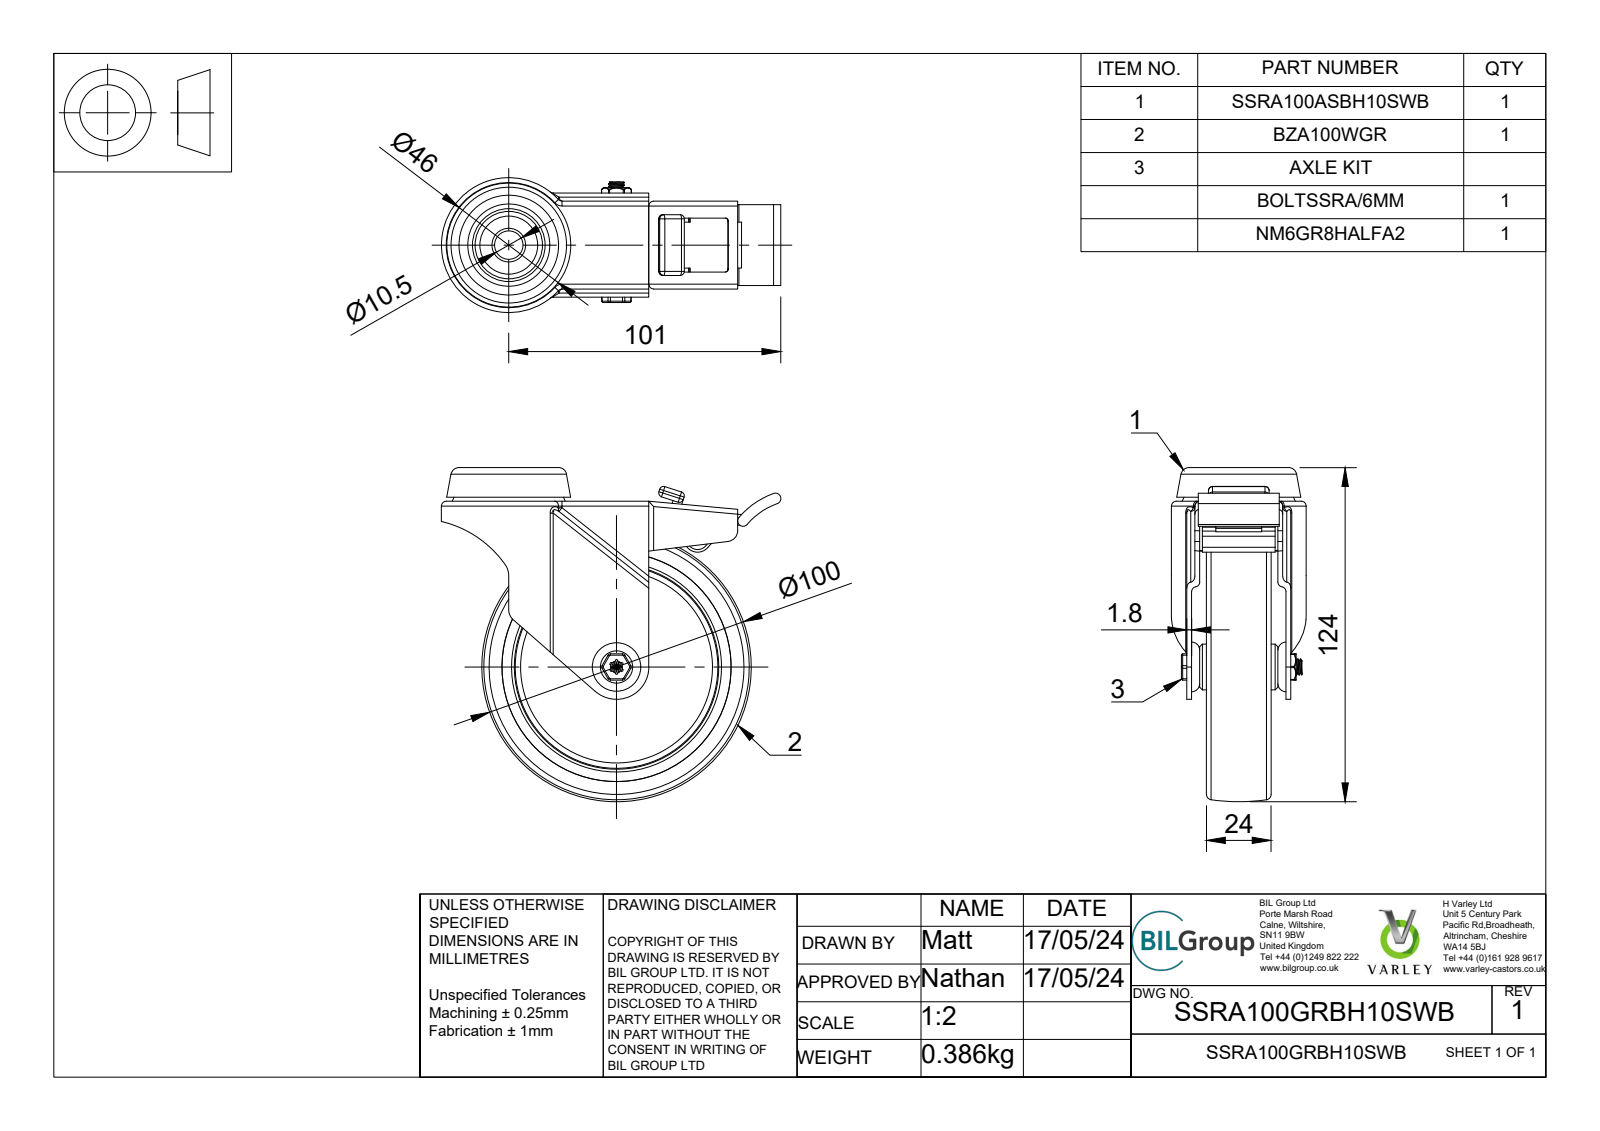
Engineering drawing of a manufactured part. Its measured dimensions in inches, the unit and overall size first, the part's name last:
Units: inches
Overall size (bounding box): 4.961 × 4.882 × 1.969
Round holes (diameter × count): ⌀0.236 ×1, ⌀0.252 ×1, ⌀0.327 ×1, ⌀0.331 ×1, ⌀0.413 ×1, ⌀0.416 ×1, ⌀1.181 ×1, ⌀3.346 ×1
Round bosses / shafts (diameter × count): ⌀1.535 ×1, ⌀0.709 ×1, ⌀0.669 ×1, ⌀0.581 ×1, ⌀0.315 ×1, ⌀0.231 ×1, ⌀0.187 ×1
Partial cylindrical surfaces — rounded edges, fillets, slot ends (radius × count): R0.071 ×27, R0.039 ×22, R0.02 ×13, R0.059 ×12, R0.016 ×6, R0.035 ×4, R0.079 ×4, R0.197 ×2
Main face-to-face distances: 0.071, 1.331, 0.354, 0.591, 0.118, 0.236, 0.453, 0.098, 0.189, 0.689
Volume: 9.257 in³ · Surface area: 129.7 in²
Bodies: 9 solids, 473 faces (199 planar, 149 cylindrical, 125 other)
Part name (STEP PRODUCT): SSRA100GRBH10SWB v4; SSRA100ASBH10SWB v1; STAINLESS STEEL HEAD (1); STAINLESS STEEL FORKS (1) (+8 more)
STEP written by: Autodesk Translation Framework v13.14.0.145 (AUTOMOTIVE_DESIGN)
